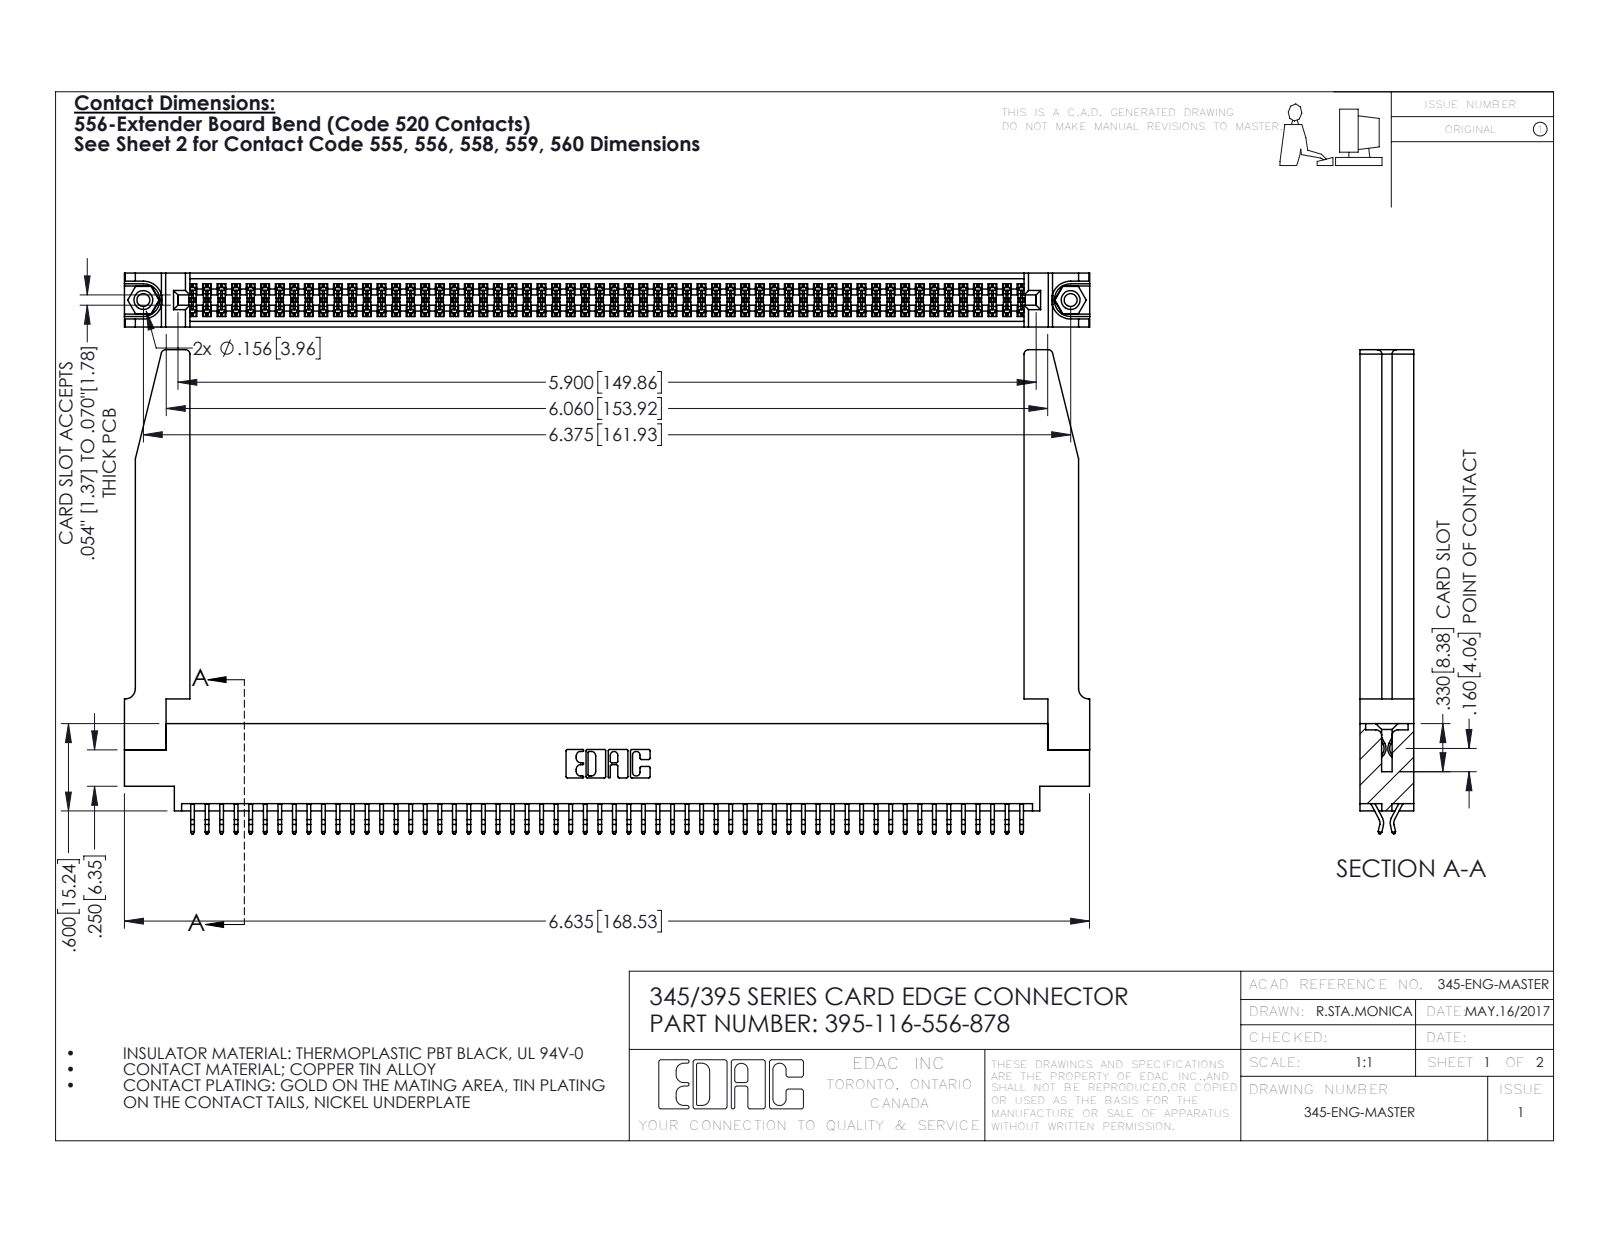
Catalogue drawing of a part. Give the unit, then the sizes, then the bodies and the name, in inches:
Units: inches
Overall size (bounding box): 6.636 × 3.327 × 0.37
Round holes (diameter × count): ⌀0.089 ×2, ⌀0.125 ×2, ⌀0.156 ×2, ⌀0.064 ×1
Round bosses / shafts (diameter × count): ⌀0.155 ×2
Partial cylindrical surfaces — rounded edges, fillets, slot ends (radius × count): R0.006 ×174, R0.01 ×22, R0.03 ×8, R0.007 ×6, R0.031 ×6, R0.026 ×3, R0.01 ×2, R0.014 ×2
Main face-to-face distances: 0.072, 0.37, 0.298, 0.025, 0.098, 0.272, 0.2, 0.225, 0.175, 0.15
Hole centre spacings: 0.27, 6.139, 6.375
Volume: 1.475 in³ · Surface area: 48.73 in²
Bodies: 121 solids, 6860 faces (4518 planar, 2290 cylindrical, 52 other)
Part name (STEP PRODUCT): 345-292-001_556 Tail; 345 Part_0.170 Offset - 0.156 Dia-TH; 395-116-556-878; 345-250-001_345-250-001-102 (+1 more)
STEP written by: SolidWorks 2016 (CONFIG_CONTROL_DESIGN)
